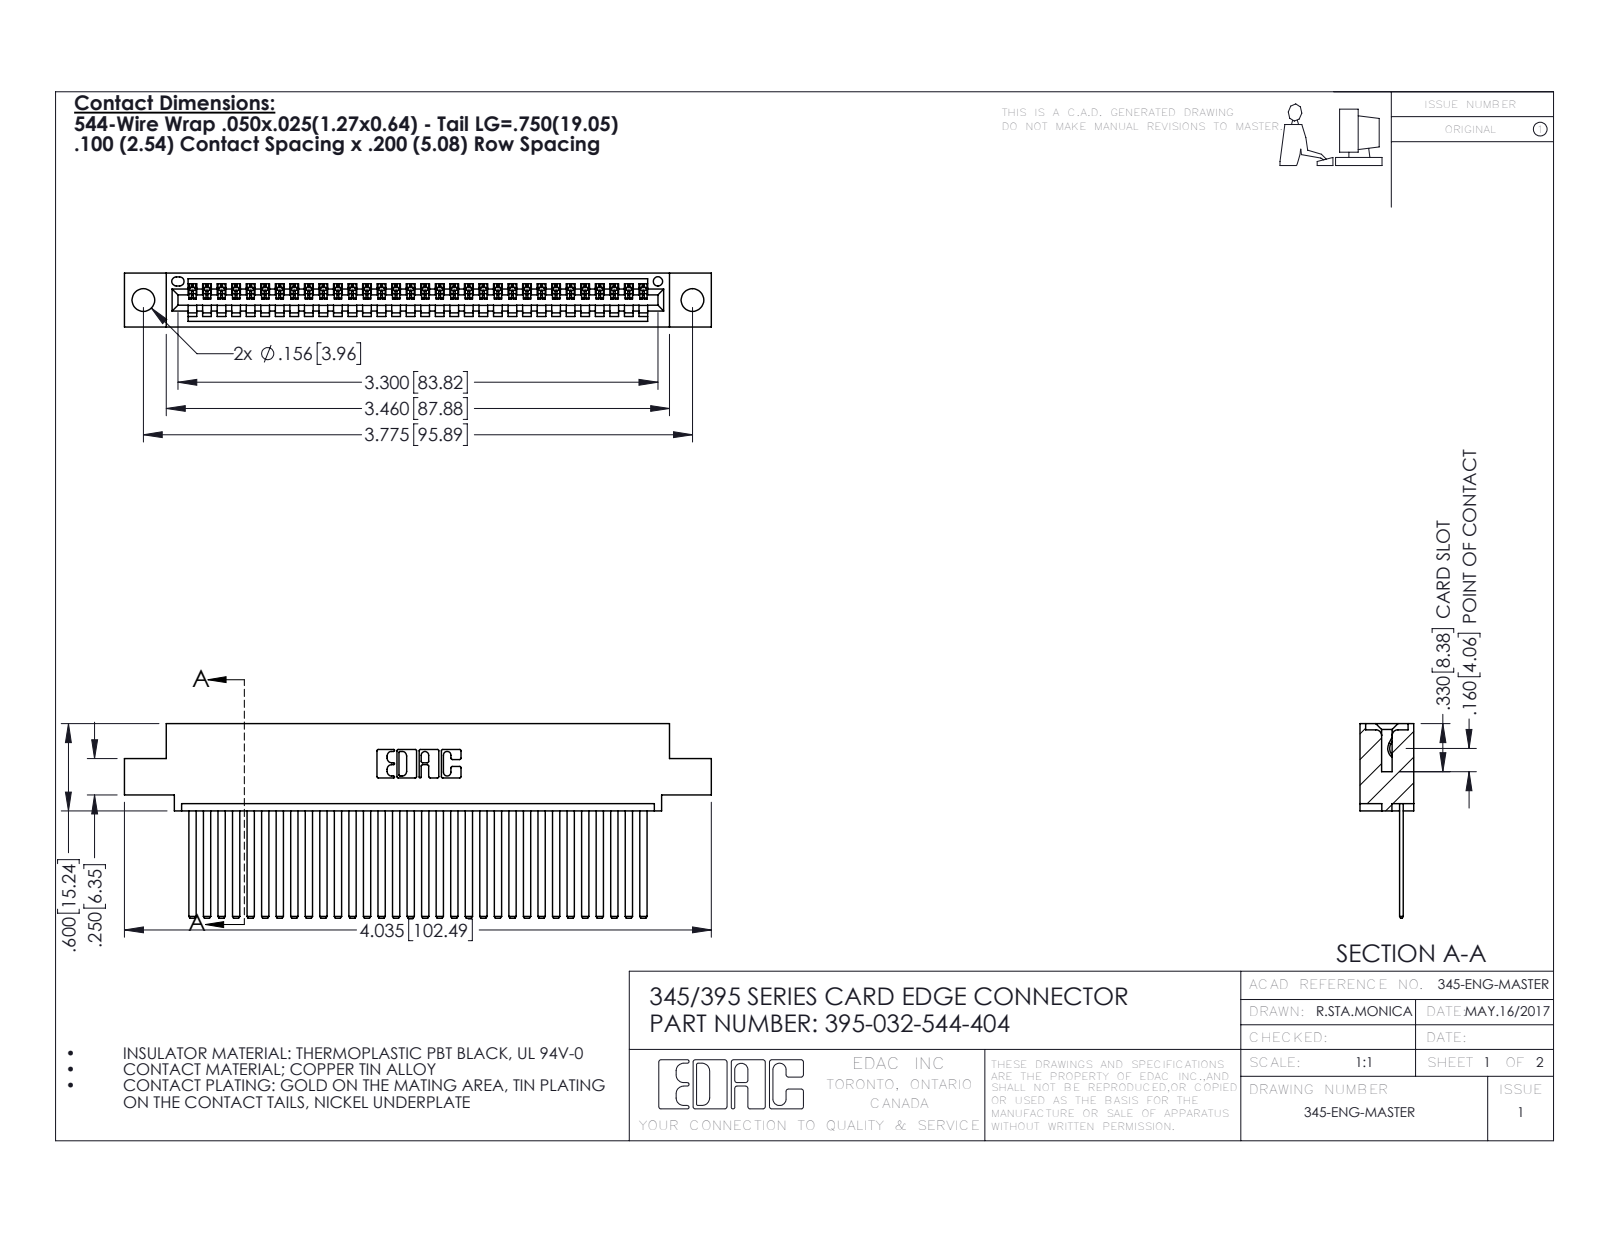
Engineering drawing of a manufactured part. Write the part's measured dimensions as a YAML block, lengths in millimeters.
part_name: "395-032-544-404; 345 Part_0.110 Offset - 0.156 Dia-TH; 345-292-001_345-293-144"
step_written_by: "SolidWorks 2016 (CONFIG_CONTROL_DESIGN)"
units: millimeters
bodies: {solids: 33, faces: 1794, planar: 1236, cylindrical: 558, other: 0}
overall_size: [102.5, 34, 9.4]
volume: 9870
surface_area: 13970
round_holes:
  - {diameter: 4, count: 2}
  - {diameter: 1.6, count: 1}
partial_cylinders:
  - {radius: 0.2, count: 64}
  - {radius: 0.3, count: 22}
  - {radius: 0.2, count: 6}
  - {radius: 0.8, count: 6}
  - {radius: 0.7, count: 3}
  - {radius: 0.8, count: 2}
  - {radius: 1, count: 2}
  - {radius: 0.4, count: 1}
face_to_face_distances: [1.8, 7.6, 0.6, 2.5, 6.9, 9.4, 5.1, 5.7, 3.8, 1.8]
hole_center_spacings: [6.9, 89.9, 95.9]
